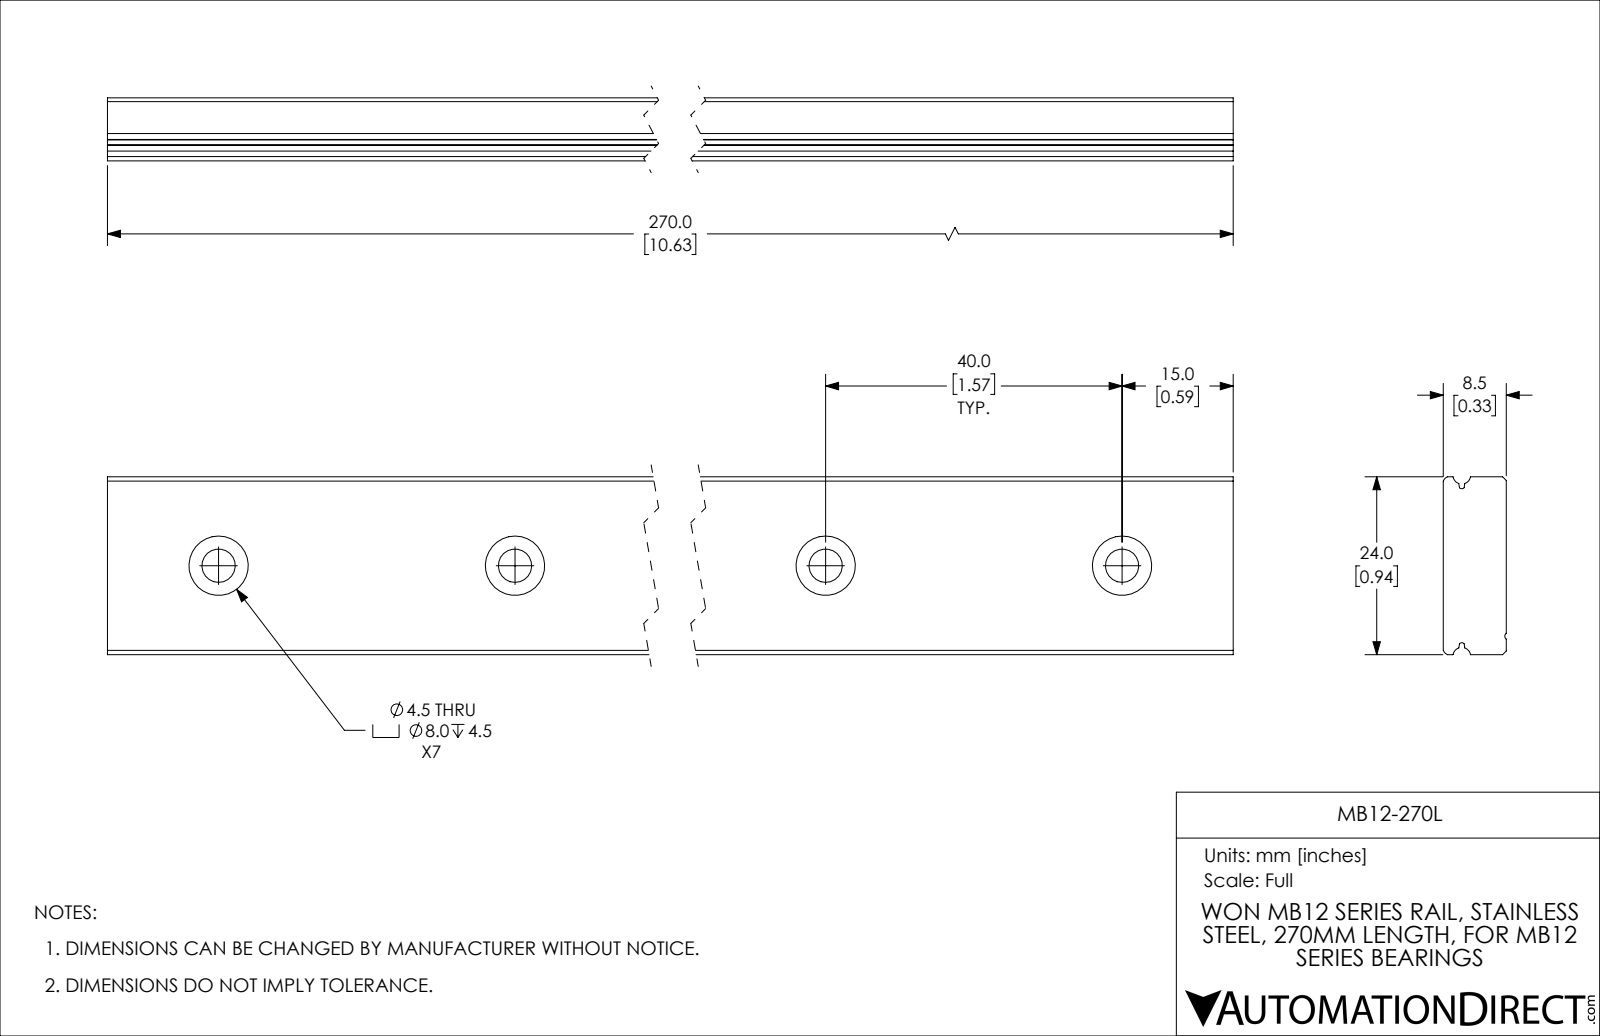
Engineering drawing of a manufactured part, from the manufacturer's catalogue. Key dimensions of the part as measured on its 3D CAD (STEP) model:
Part name (STEP PRODUCT): MB12-270L
STEP written by: SolidWorks 2019 (CONFIG_CONTROL_DESIGN)
Units: millimetres
Bodies: 1 solid, 60 faces (22 planar, 38 cylindrical, 0 other)
Overall size (bounding box): 270 × 24 × 8.5
Volume: 51 709 mm³ · Surface area: 19 704 mm²
Round holes (diameter × count): ⌀4.5 ×7, ⌀8 ×7
Partial cylindrical surfaces — rounded edges, fillets, slot ends (radius × count): R0.42 ×2, R1.15 ×2, R1.2 ×2, R0.5 ×1
Main face-to-face distances: 8.5, 24, 2.21, 4, 4.5, 270
Hole centre spacings: 40, 80, 120, 160, 200, 240
